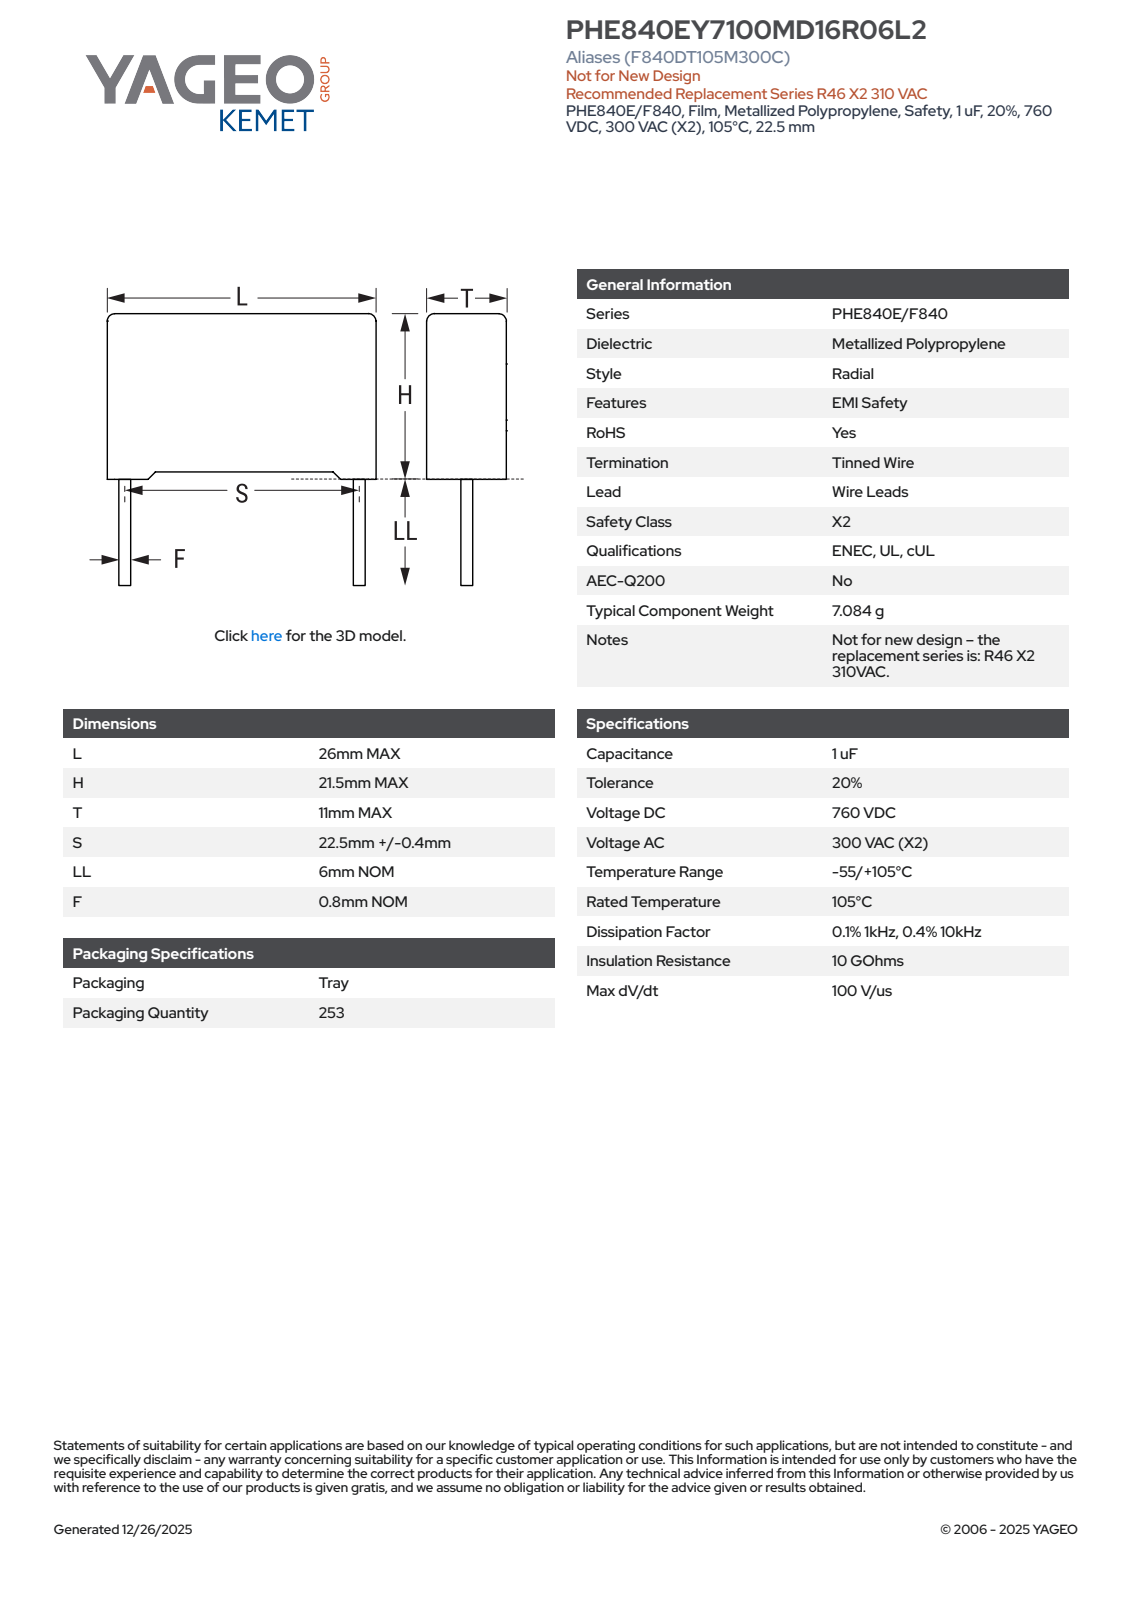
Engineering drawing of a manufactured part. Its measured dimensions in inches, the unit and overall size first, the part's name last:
Units: inches
Overall size (bounding box): 1.083 × 1.024 × 0.433
Round bosses / shafts (diameter × count): ⌀0.031 ×2
Partial cylindrical surfaces — rounded edges, fillets, slot ends (radius × count): R0.02 ×4
Main face-to-face distances: 0.433, 1.024, 0.817, 0.817, 0.029, 0.03, 0.846, 0.034, 0.989, 0.399
Volume: 0.364 in³ · Surface area: 3.452 in²
Bodies: 4 solids, 85 faces (77 planar, 8 cylindrical, 0 other)
Part name (STEP PRODUCT): CFR_RB2_26X21.5X11_L26H21.5T11S22.5LL6F0.8
STEP written by: SolidWorks 2021 (AUTOMOTIVE_DESIGN)
